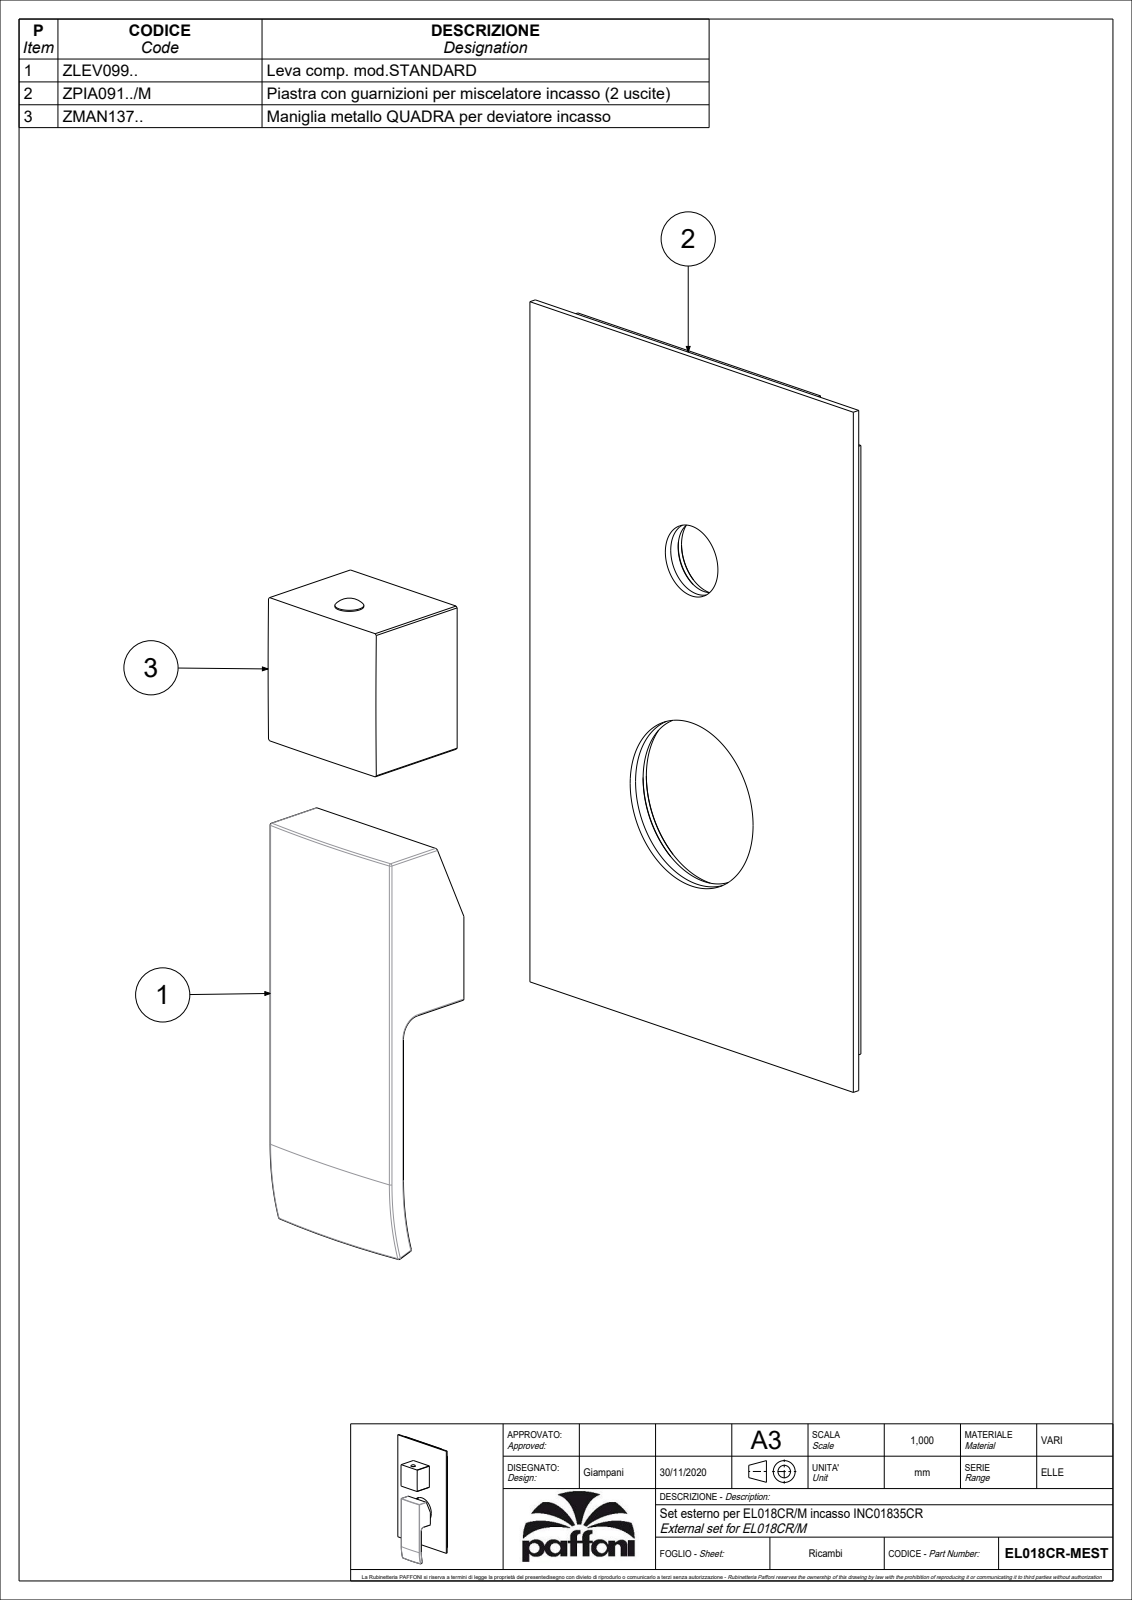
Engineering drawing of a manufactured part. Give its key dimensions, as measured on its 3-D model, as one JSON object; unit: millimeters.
{"part_name": "EL018CR-MEST", "step_written_by": "CREO PARAMETRIC BY PTC INC, 2020044 (CONFIG_CONTROL_DESIGN)", "units": "millimeters", "bodies": {"solids": 3, "faces": 279, "planar": 111, "cylindrical": 105, "other": 63}, "overall_size": [212.38, 120, 39.99], "volume_mm3": 110539, "surface_area_mm2": 82574, "round_holes": [[3, 2], [5.5, 2], [3.2, 1], [3.3, 1], [4.2, 1], [7.8, 1], [14.8, 1], [19.5, 1], [21.5, 1], [25, 1], [36, 1], [45.6, 1]], "round_bosses_or_shafts": [[7.6, 2], [54.6, 1], [28.5, 1], [5, 1]], "partial_cylinders_radius": [[1.5, 14], [0.5, 10], [2, 4], [300, 2], [2.25, 1], [28, 1]], "face_to_face_distances": [2, 2.8, 0.8, 40, 42.5, 2.5, 45, 30, 37.5, 29.2], "hole_center_spacings": [7, 10, 58, 68]}
